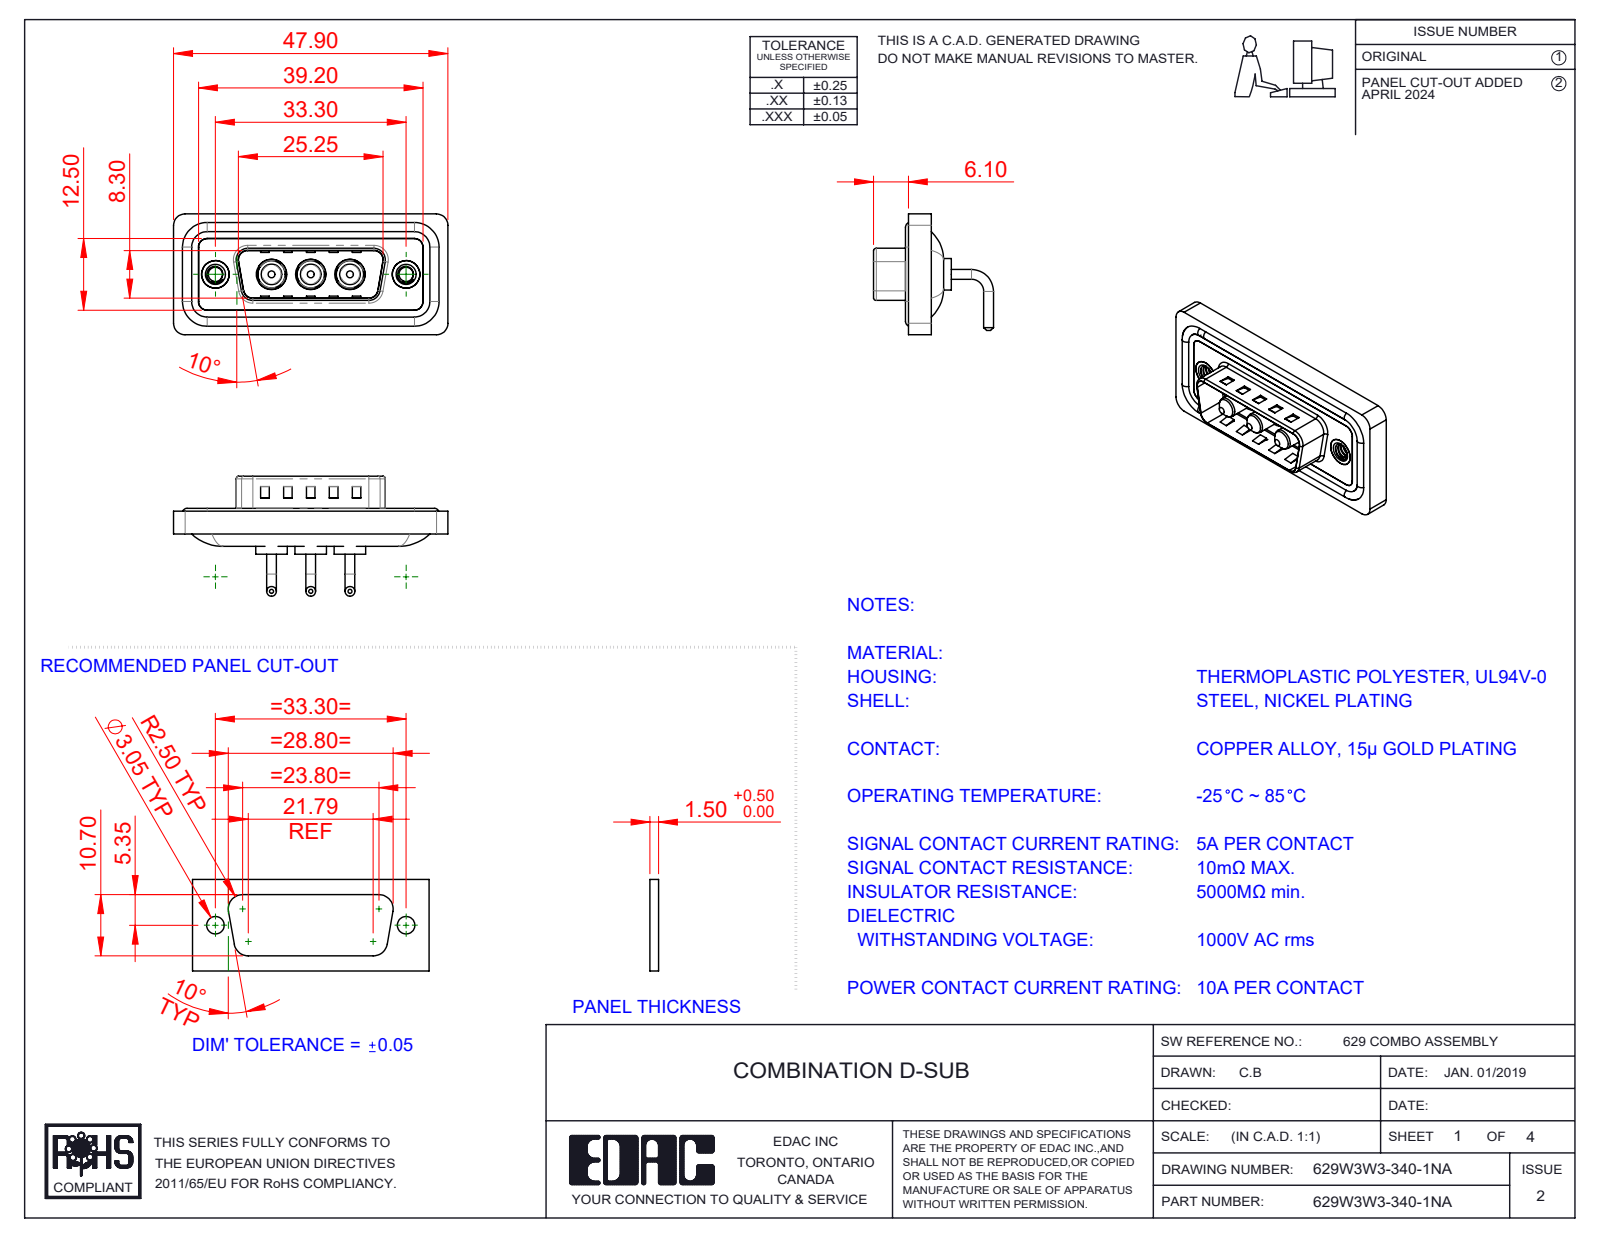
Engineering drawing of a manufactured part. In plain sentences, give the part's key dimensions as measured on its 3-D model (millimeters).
The part is named "629Combo Threaded Rivet_A; 629Combo Shell Front_15 Contacts; 629W3W3-340-1NA; 629Combo Housing_3W3 (+3 more)". Its 3-D file was written by "SolidWorks 2023 (CONFIG_CONTROL_DESIGN)". It is 13 solids with 570 faces: 207 planar, 245 cylindrical and 118 other. Overall it measures 47.9 by 21.1 by 20.95 millimeters. Its volume is 5 608 cubic millimeters and its surface area 8 887 square millimeters. Round holes: 3 of diameter 4.85, 3 of diameter 5.3, 2 of diameter 2.5, 2 of diameter 4, 2 of diameter 4.8, 2 of diameter 5. Round bosses or shafts: 6 of diameter 1.7, 4 of diameter 1.6, 3 of diameter 5.5, 3 of diameter 5.2, 3 of diameter 4.75, 3 of diameter 3.75, 3 of diameter 3.6, 2 of diameter 4.9. Partial cylindrical surfaces (rounded edges, fillets, slot ends): 20 of radius 2, 18 of radius 1.5, 8 of radius 0.5, 8 of radius 1.6, 4 of radius 0.25, 4 of radius 0.6, 4 of radius 0.65, 4 of radius 0.9. The main face-to-face distances are 0.4, 2.9, 0.8, 1.1, 2.1, 1.6, 3.1, 2.5, 4.5, 1.5. The hole center spacings are 6.85, 9.8, 16.65, 23.5, 13.7, 33.3.
